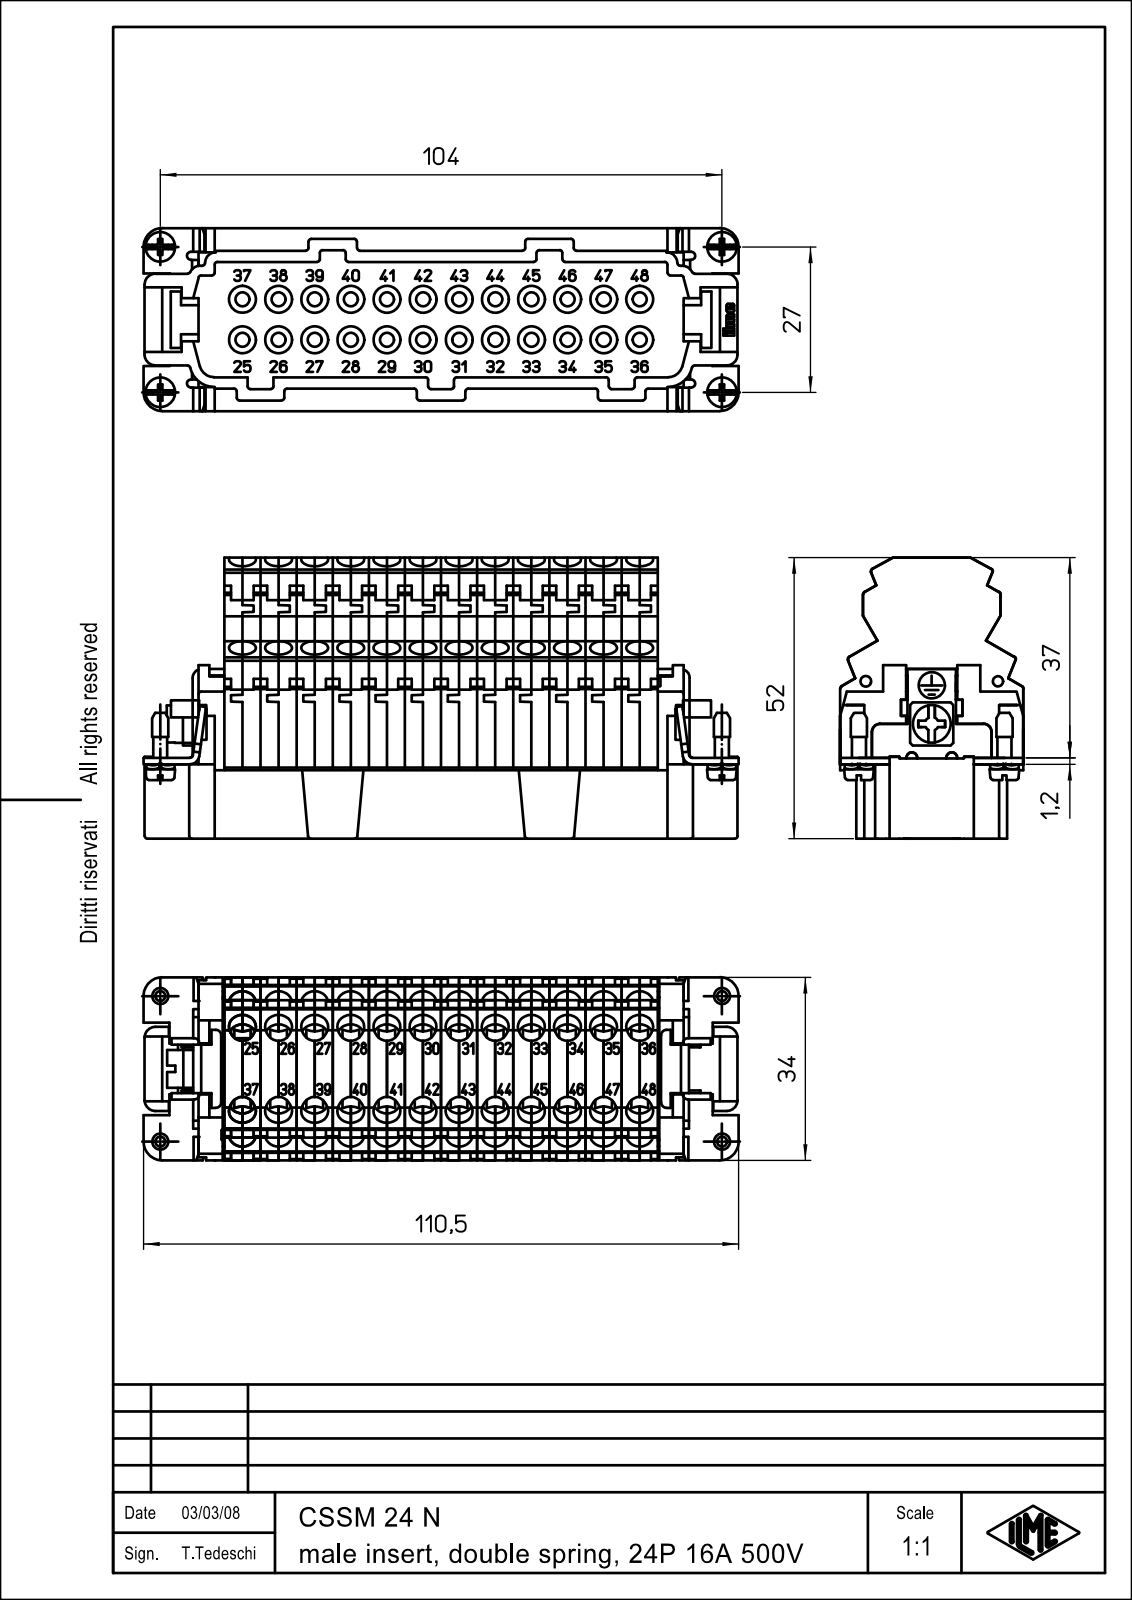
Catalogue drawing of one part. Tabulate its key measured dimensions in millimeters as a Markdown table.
| quantity | value |
| --- | --- |
| part name | PIAST_1; PIAST_2; CORPO; CSSM_24_N |
| STEP written by | PTC Creo Elements/Direct Modeling 19.0B 21-Mar-2015 (C) Parametric Technology GmbH (AUTOMOTIVE_DESIGN) |
| units | millimeters |
| bodies | 3 solids, 1803 faces (1093 planar, 392 cylindrical, 318 other) |
| overall size | 110.4 × 51.7 × 34 |
| volume | 95 383 mm³ |
| surface area | 40 465 mm² |
| round holes (diameter × count) | 5 × 48, 2.6 × 24, 2.8 × 4, 4.2 × 1 |
| round bosses / shafts (diameter × count) | 3.8 × 24, 2.5 × 24, 5.5 × 4, 3 × 4, 2.6 × 4, 7 × 1 |
| partial cylindrical surfaces (radius × count) | 1 × 23, 0.5 × 8, 2 × 8, 0.75 × 4, 3.5 × 4, 1.2 × 2, 1.3 × 2, 2.5 × 2 |
| main face-to-face distances | 6.3, 27.7, 12, 10.08, 3, 85.2, 34, 1.2, 4.8, 1.5 |
| hole center spacings | 6.7, 13.4, 20.1, 26.8, 33.5, 17.99, 23.41, 40.2 |
